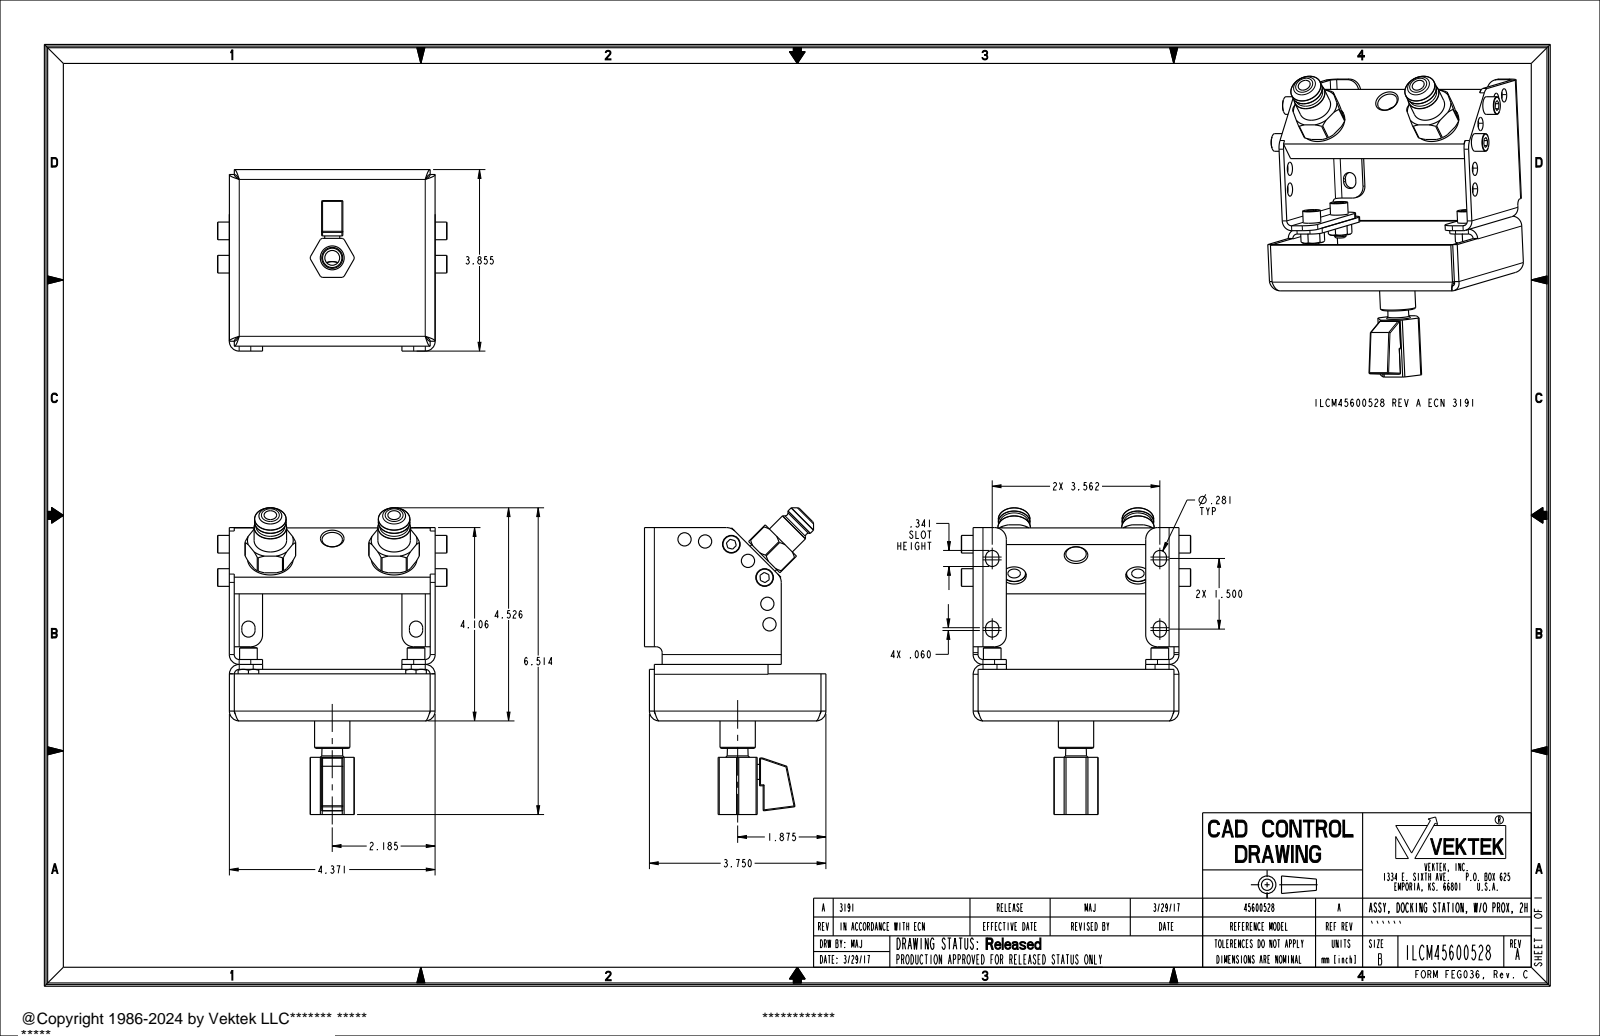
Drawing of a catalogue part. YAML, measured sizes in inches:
part_name: "ILCM45600528"
step_written_by: "PRO/ENGINEER BY PARAMETRIC TECHNOLOGY CORPORATION, 2013320 (AUTOMOTIVE_DESIGN)"
units: inches
bodies: {solids: 3, faces: 564, planar: 236, cylindrical: 162, other: 166}
overall_size: [6.446, 5.818, 4.874]
volume: 11.02
surface_area: 150.7
round_holes:
  - {diameter: 0.281, count: 5}
  - {diameter: 0.266, count: 2}
  - {diameter: 0.515, count: 2}
  - {diameter: 0.97, count: 2}
  - {diameter: 0.315, count: 1}
  - {diameter: 0.433, count: 1}
  - {diameter: 0.443, count: 1}
  - {diameter: 0.781, count: 1}
round_bosses_or_shafts:
  - {diameter: 0.375, count: 6}
  - {diameter: 0.25, count: 4}
  - {diameter: 0.75, count: 3}
  - {diameter: 0.69, count: 2}
  - {diameter: 0.671, count: 2}
  - {diameter: 0.319, count: 1}
partial_cylinders:
  - {radius: 0.02, count: 18}
  - {radius: 0.105, count: 10}
  - {radius: 0.209, count: 10}
  - {radius: 0.25, count: 10}
  - {radius: 0.141, count: 8}
  - {radius: 0.2, count: 4}
  - {radius: 0.536, count: 2}
  - {radius: 0.125, count: 1}
face_to_face_distances: [0.105, 4.269, 4.268, 3.645, 4.374, 0.106, 4.163, 4.165, 0.103, 4.372]
hole_center_spacings: [0.439, 1, 1.423, 1.45, 2.229, 1.871, 2.553, 2.63]
